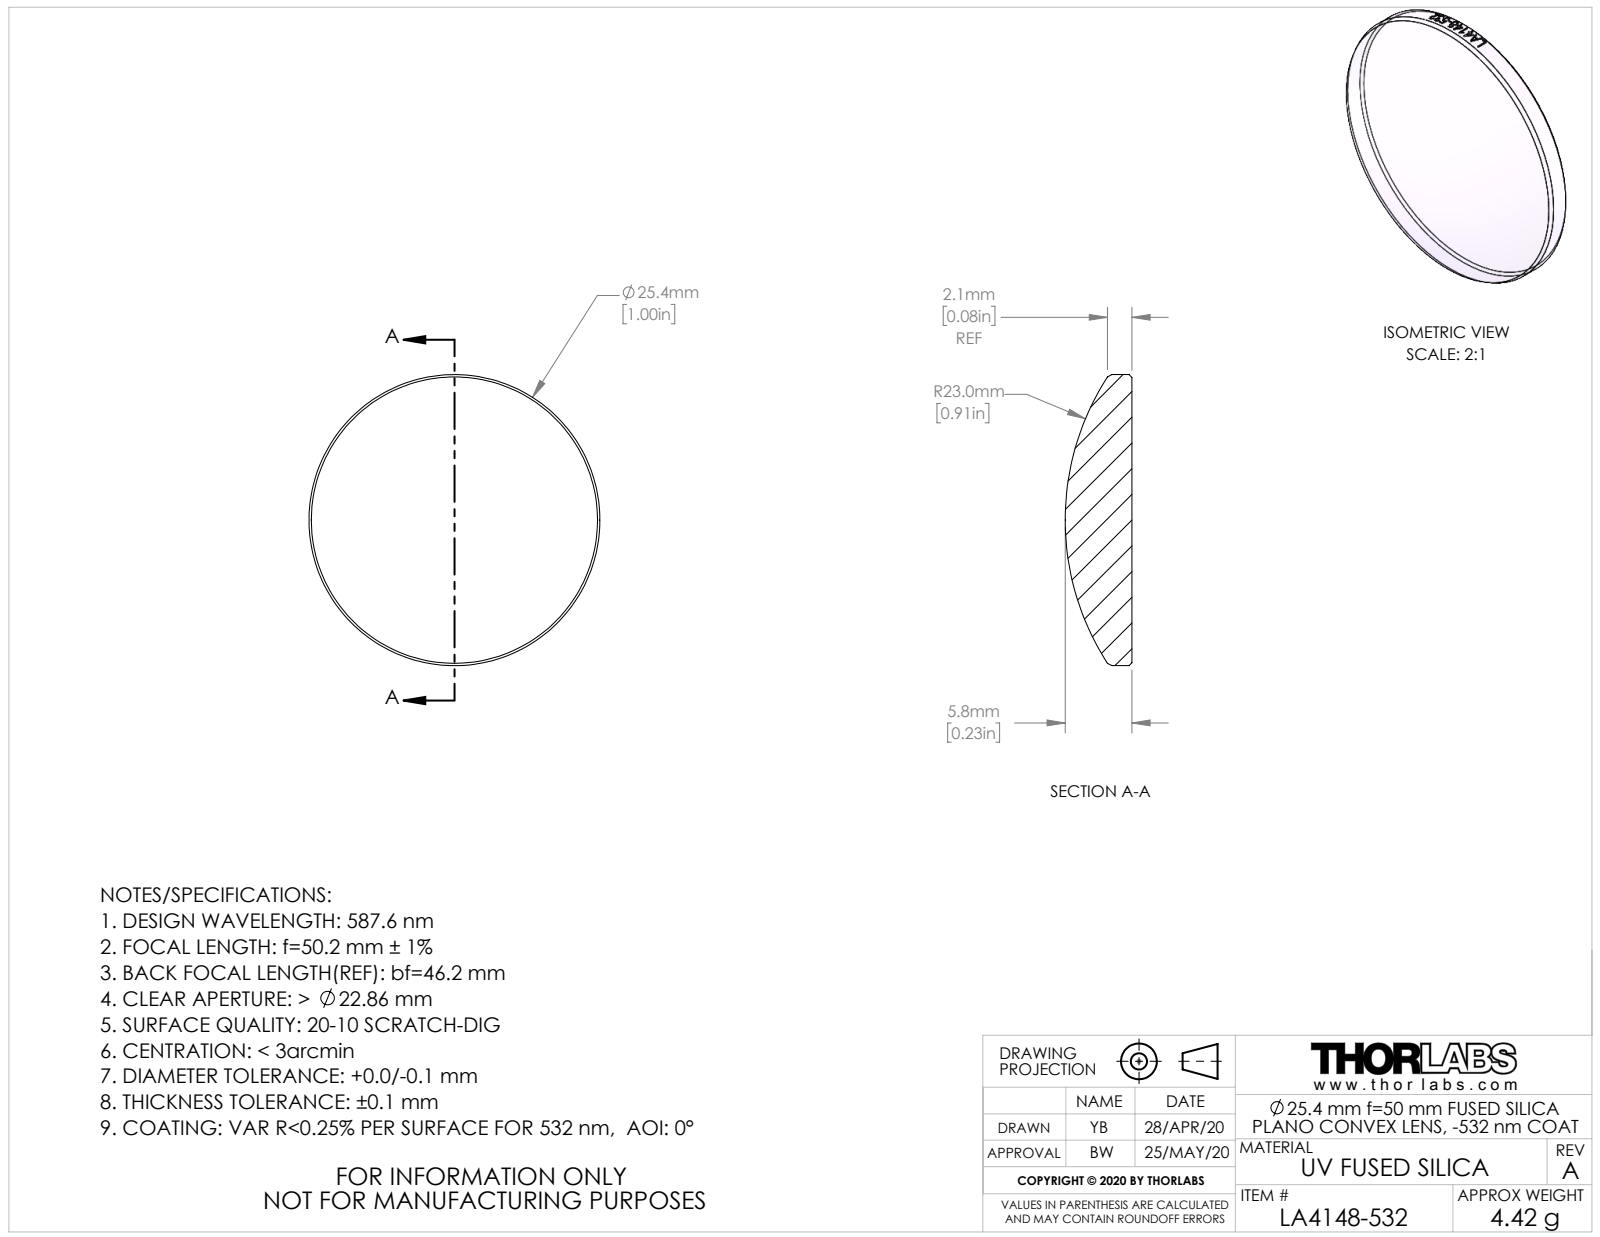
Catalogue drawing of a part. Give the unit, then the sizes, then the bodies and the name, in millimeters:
Units: millimetres
Overall size (bounding box): 25.4 × 25.4 × 5.82
Round bosses / shafts (diameter × count): ⌀25.4 ×1
Volume: 2 006 mm³ · Surface area: 1 202 mm²
Bodies: 1 solid, 24 faces (1 planar, 17 cylindrical, 6 other)
Part name (STEP PRODUCT): CTN015734-E0W
STEP written by: SolidWorks 2018 (AUTOMOTIVE_DESIGN)
